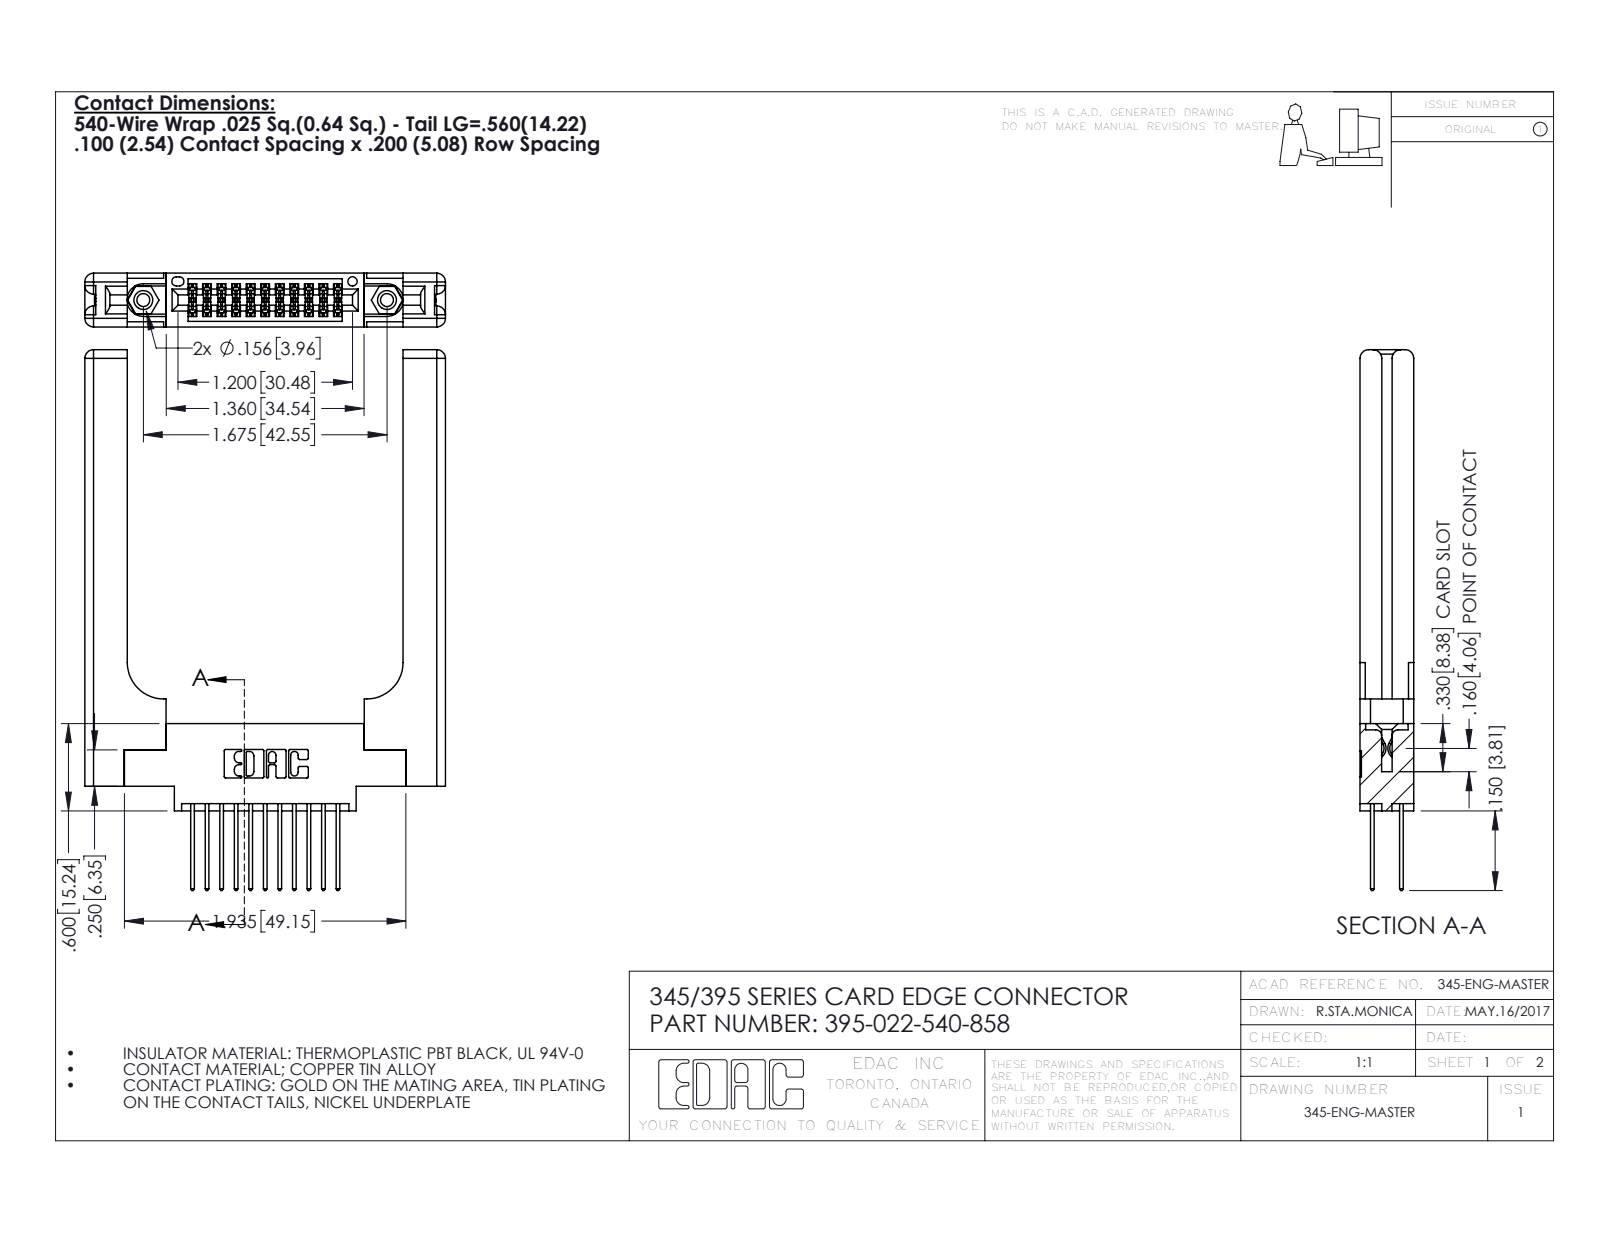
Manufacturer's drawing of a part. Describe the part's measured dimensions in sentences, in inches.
The part is named "345 Part_0.170 Offset - 0.156 Dia-TH; 345-220-058_345-220-058; 395-022-540-858; 345-250-001_345-250-001-102 (+1 more)". Its 3-D file was written by "SolidWorks 2016 (CONFIG_CONTROL_DESIGN)". It is 27 solids with 1486 faces: 958 planar, 468 cylindrical and 60 other. Overall it measures 3.717 by 2.479 by 0.37 inches. Its volume is 0.871 cubic inches and its surface area 21.02 square inches. Round holes: 2 of diameter 0.089, 2 of diameter 0.125, 2 of diameter 0.156, 1 of diameter 0.064. Round bosses or shafts: 2 of diameter 0.155. Partial cylindrical surfaces (rounded edges, fillets, slot ends): 33 of radius 0.006, 22 of radius 0.01, 22 of radius 0.01, 16 of radius 0.06, 6 of radius 0.007, 6 of radius 0.031, 3 of radius 0.026, 2 of radius 0.014. The main face-to-face distances are 0.37, 0.072, 0.298, 0.148, 0.15, 0.077, 0.22, 0.123, 0.098, 0.272. The hole center spacings are 0.27, 1.443, 1.675.
